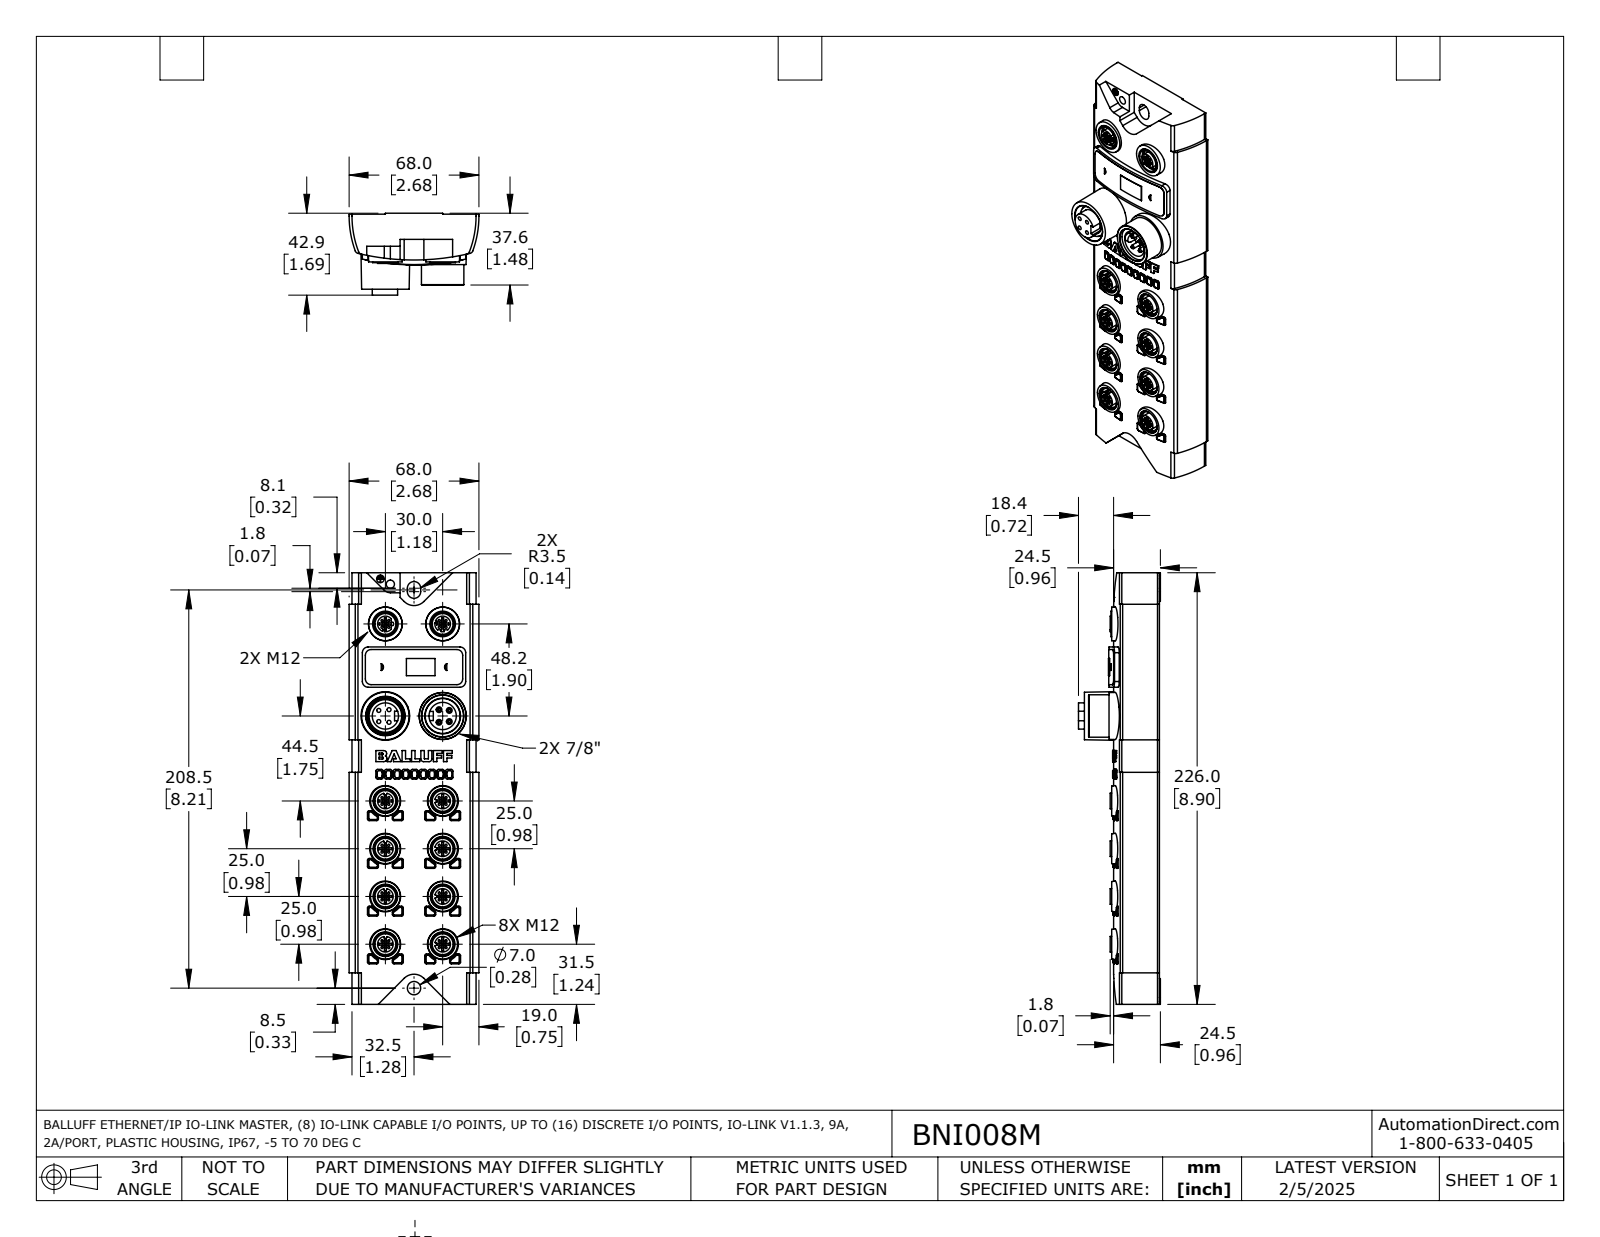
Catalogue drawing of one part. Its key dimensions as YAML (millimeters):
part_name: "BNI008M"
step_written_by: "SolidWorks 2021 (AUTOMOTIVE_DESIGN)"
units: millimeters
bodies: {solids: 1, faces: 1371, planar: 596, cylindrical: 686, other: 89}
overall_size: [226, 68, 42.9]
volume: 338200
surface_area: 56180
round_holes:
  - {diameter: 1.1, count: 50}
  - {diameter: 10.9, count: 10}
  - {diameter: 12.3, count: 8}
  - {diameter: 2.1, count: 4}
  - {diameter: 12, count: 2}
  - {diameter: 4, count: 1}
  - {diameter: 4.3, count: 1}
  - {diameter: 7, count: 1}
  - {diameter: 14.3, count: 1}
  - {diameter: 18.3, count: 1}
  - {diameter: 20.3, count: 1}
round_bosses_or_shafts:
  - {diameter: 8.2, count: 9}
  - {diameter: 3, count: 4}
  - {diameter: 2, count: 4}
  - {diameter: 13.4, count: 2}
  - {diameter: 22.2, count: 1}
  - {diameter: 18, count: 1}
  - {diameter: 13.7, count: 1}
  - {diameter: 10, count: 1}
partial_cylinders:
  - {radius: 0.3, count: 80}
  - {radius: 0.9, count: 80}
  - {radius: 0.9, count: 72}
  - {radius: 1, count: 40}
  - {radius: 0.2, count: 16}
  - {radius: 0.7, count: 8}
  - {radius: 3, count: 8}
  - {radius: 8.6, count: 8}
face_to_face_distances: [226, 25, 13.2, 11.8, 16.9, 3.7, 8.1, 8.9, 17.4, 25.8]
hole_center_spacings: [2.5, 3.5, 50, 30, 5, 28.3, 31.8, 58.3]
